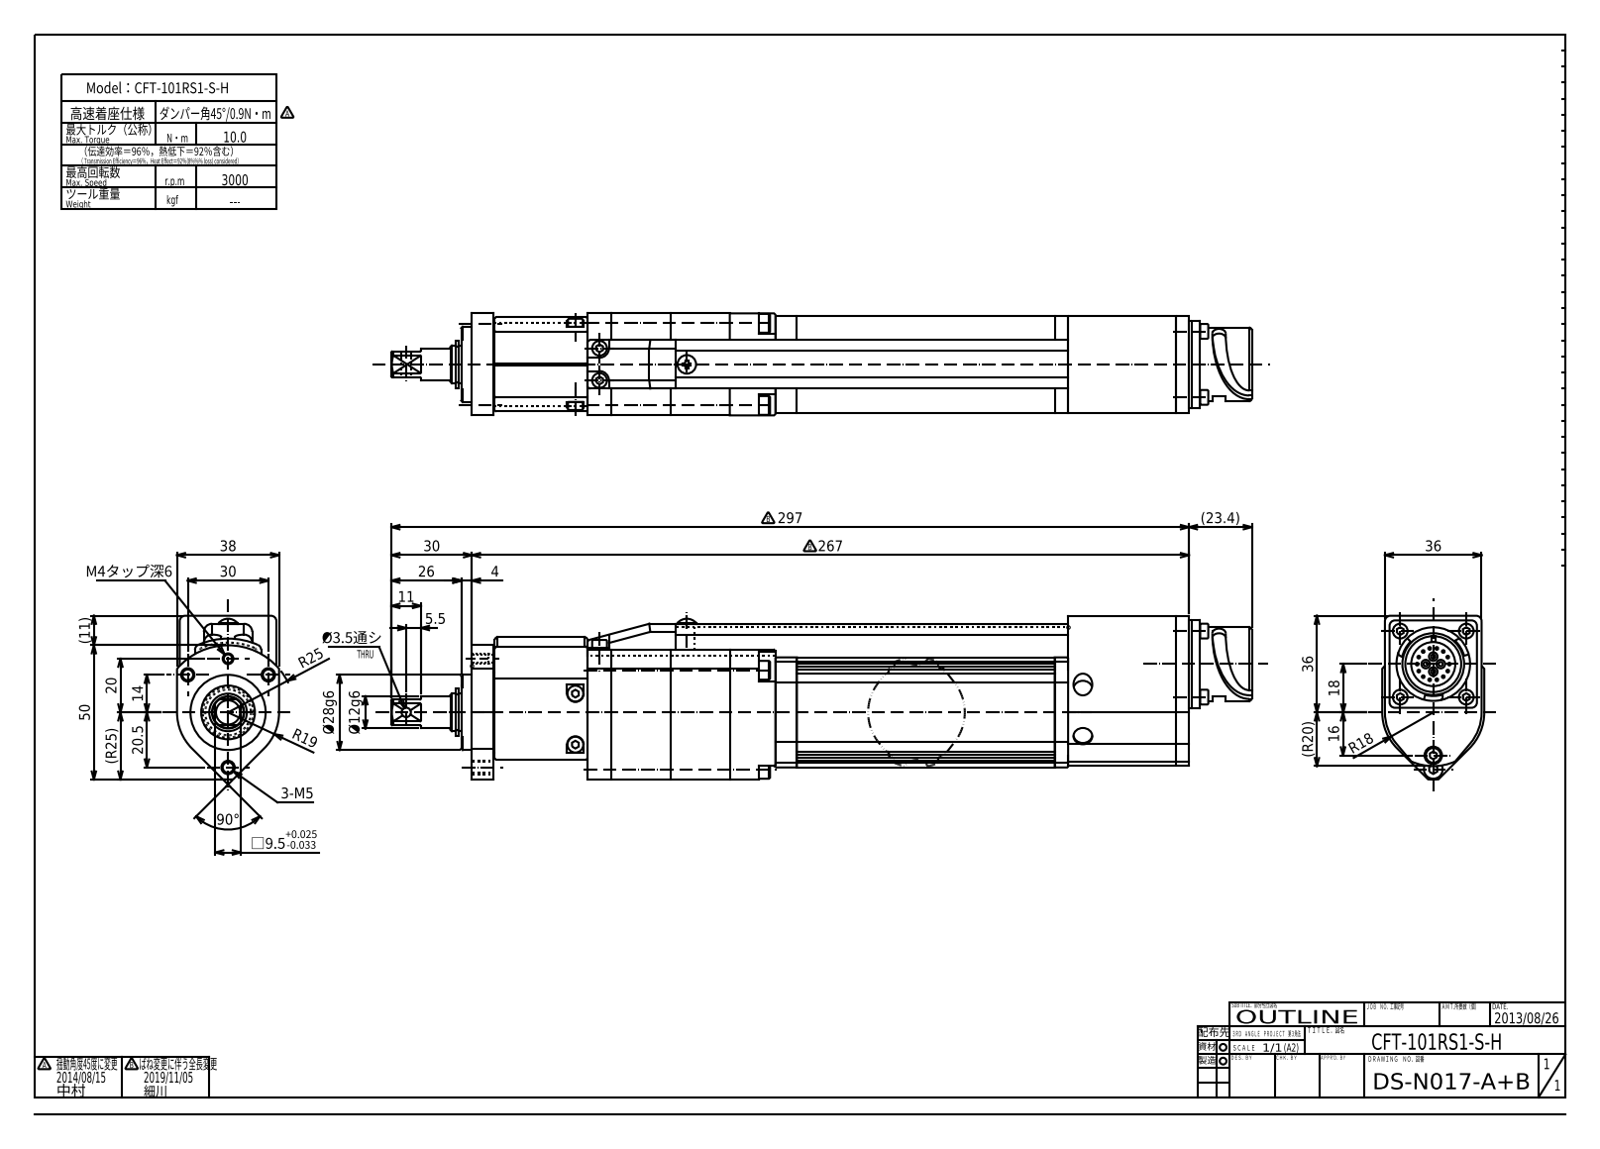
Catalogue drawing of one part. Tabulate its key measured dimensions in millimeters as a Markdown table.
| quantity | value |
| --- | --- |
| part name | CFT-101RS1-S-H_(DS-N017-C+E)_OUTLINE_20201120 |
| STEP written by | Autodesk Inventor 2021 (AUTOMOTIVE_DESIGN) |
| units | millimeters |
| bodies | 1 solid, 697 faces (429 planar, 192 cylindrical, 76 other) |
| overall size | 320.4 × 61 × 38 |
| volume | 406 344 mm³ |
| surface area | 60 764 mm² |
| round holes (diameter × count) | 4.13 × 3, 1.2 × 2, 7 × 2, 3.24 × 1, 3.5 × 1, 6.5 × 1, 14.7 × 1, 20 × 1, 20.8 × 1 |
| round bosses / shafts (diameter × count) | 1 × 14, 5.5 × 13, 4.5 × 4, 1.6 × 4, 7 × 3, 4 × 3, 6 × 2, 30 × 1 |
| partial cylindrical surfaces (radius × count) | 0.3 × 8, 3 × 7, 2 × 6, 4 × 5, 0.5 × 4, 2.75 × 4, 3.25 × 4, 1 × 3 |
| main face-to-face distances | 1, 27, 9, 10, 28, 37, 36, 3, 12.5, 0.5 |
| hole center spacings | 7.76, 8.74, 13.16, 15.52, 16.16, 20.52, 25.11, 25.57 |
